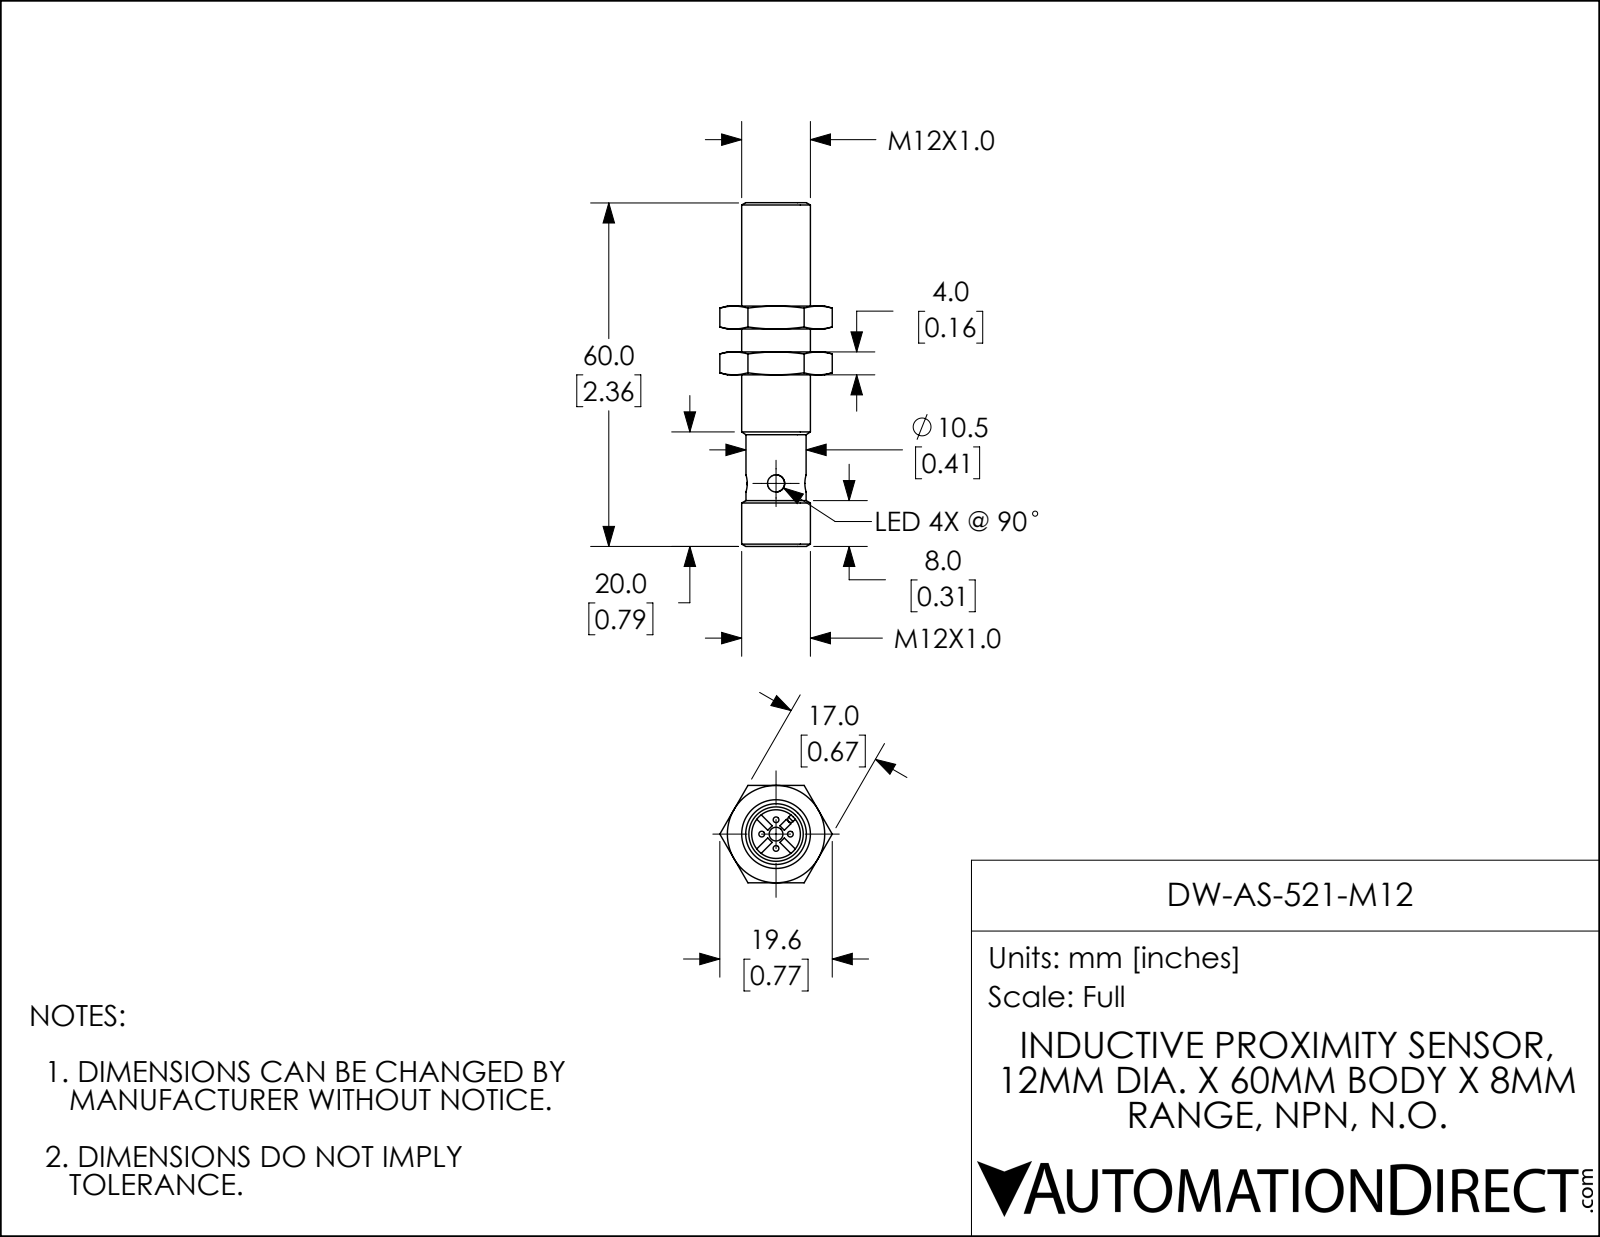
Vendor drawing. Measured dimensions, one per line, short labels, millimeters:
name: DW-AS-521-M12
written by: SolidWorks 2018 (AUTOMOTIVE_DESIGN)
unit: mm
bodies: 3 solids, 104 faces (46 planar, 19 cylindrical, 39 other)
size: 60 × 19.6 × 17
volume: 7 190 mm³; area: 4 120 mm²
holes: 2× ⌀3, 1× ⌀2.4, 1× ⌀8.5, 1× ⌀10.5, 1× ⌀10.9
bosses: 4× ⌀1, 1× ⌀12, 1× ⌀10.5, 1× ⌀10.3
rounds: 2× R0.6
face distances: 4, 8, 17, 12, 30, 26.1, 22, 18.1, 21.3, 25.2
